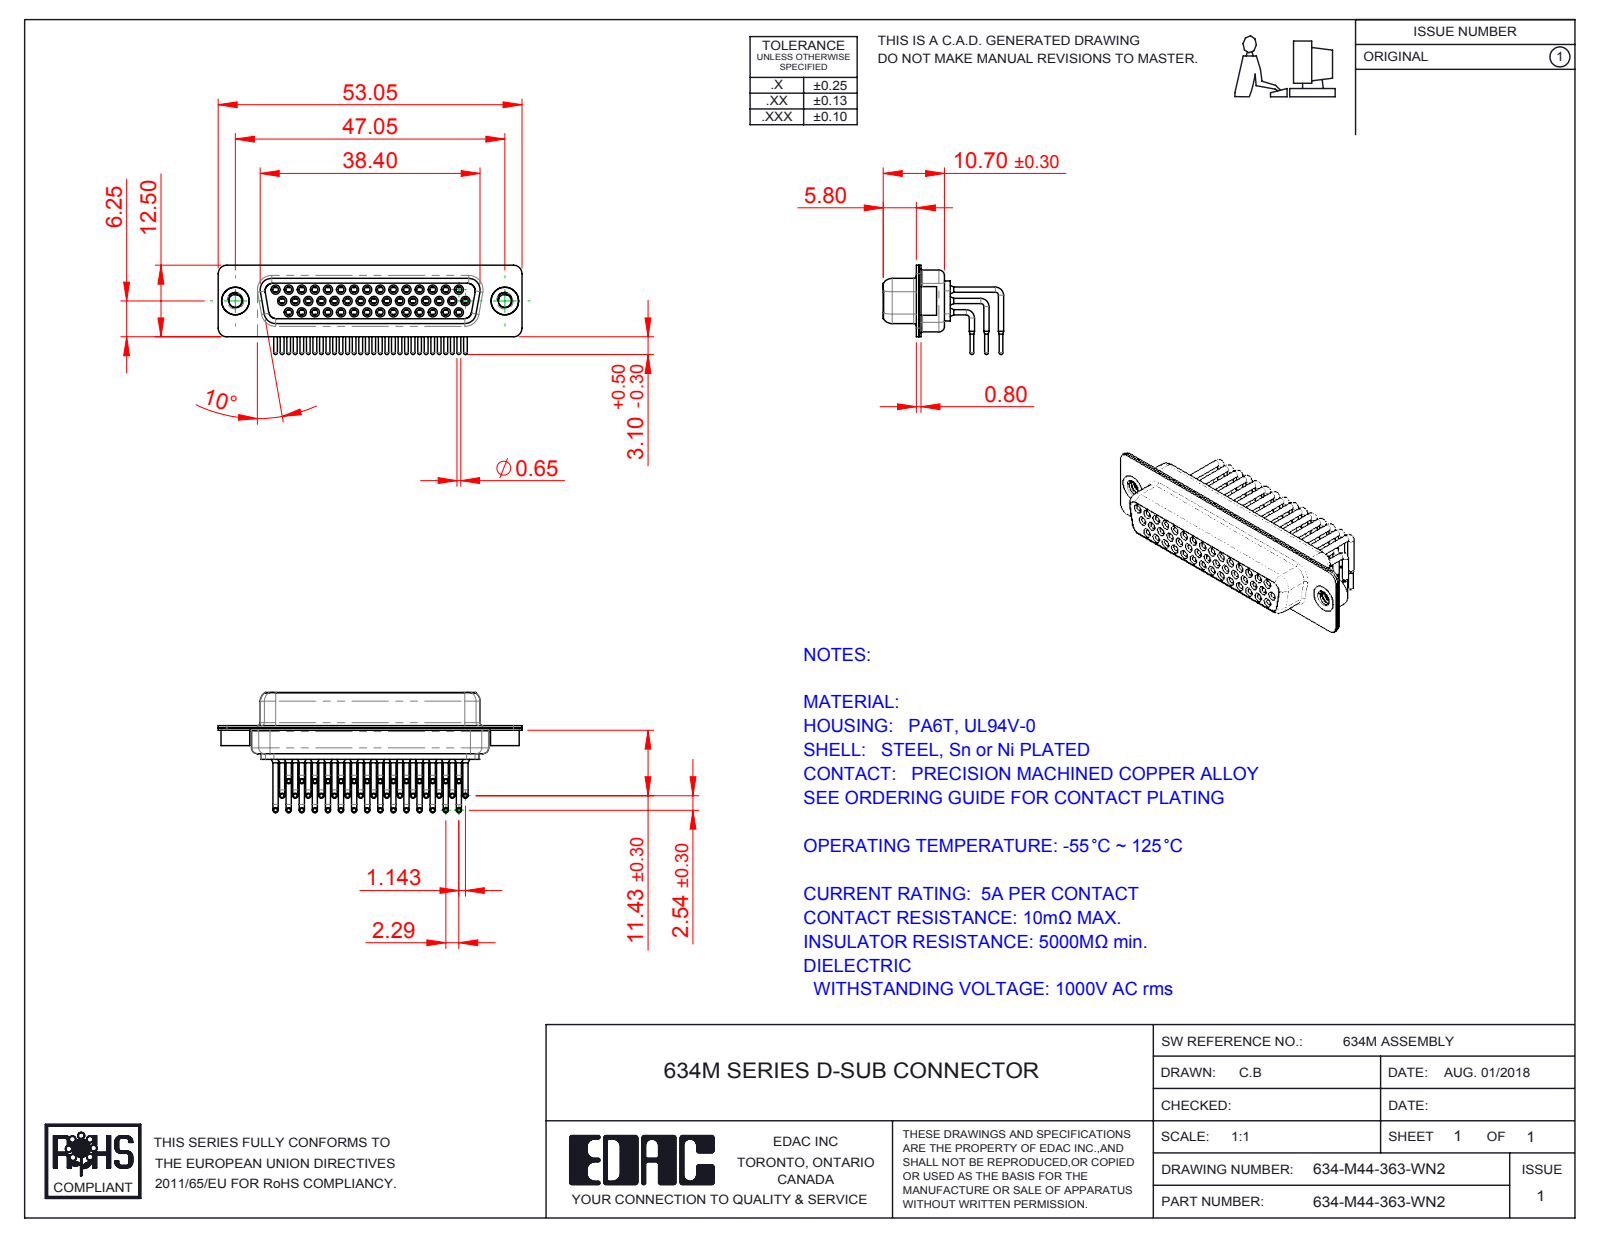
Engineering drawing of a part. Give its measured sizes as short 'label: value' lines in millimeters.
name: 634M 4-40 Threaded Rivet; 634M Contact Row 2; 634-M44-363-WN2; 634M Shell Front_44 Contacts (+4 more)
written by: SolidWorks 2016 (CONFIG_CONTROL_DESIGN)
unit: mm
bodies: 49 solids, 2611 faces (727 planar, 1149 cylindrical, 735 other)
size: 53.05 × 21.02 × 15.6
volume: 3 837 mm³; area: 13 038 mm²
holes: 44× ⌀1, 44× ⌀1.1, 44× ⌀1.7, 44× ⌀1.8, 44× ⌀2, 2× ⌀2.26, 2× ⌀4, 2× ⌀4.8
bosses: 88× ⌀0.9, 44× ⌀1.6, 44× ⌀1.5, 44× ⌀0.65, 2× ⌀5, 2× ⌀4.9
rounds: 16× R1.5, 12× R2, 8× R1.35, 8× R1.6, 4× R0.25, 4× R0.5, 4× R0.6, 4× R0.65
face distances: 0.4, 1.45, 8.95, 2.3, 1.9, 8.5, 6.2, 7.05, 0.45, 0.85
hole spacings: 2.28, 3.96, 2.29, 4.57, 8.24, 6.86, 11.43, 10.48
